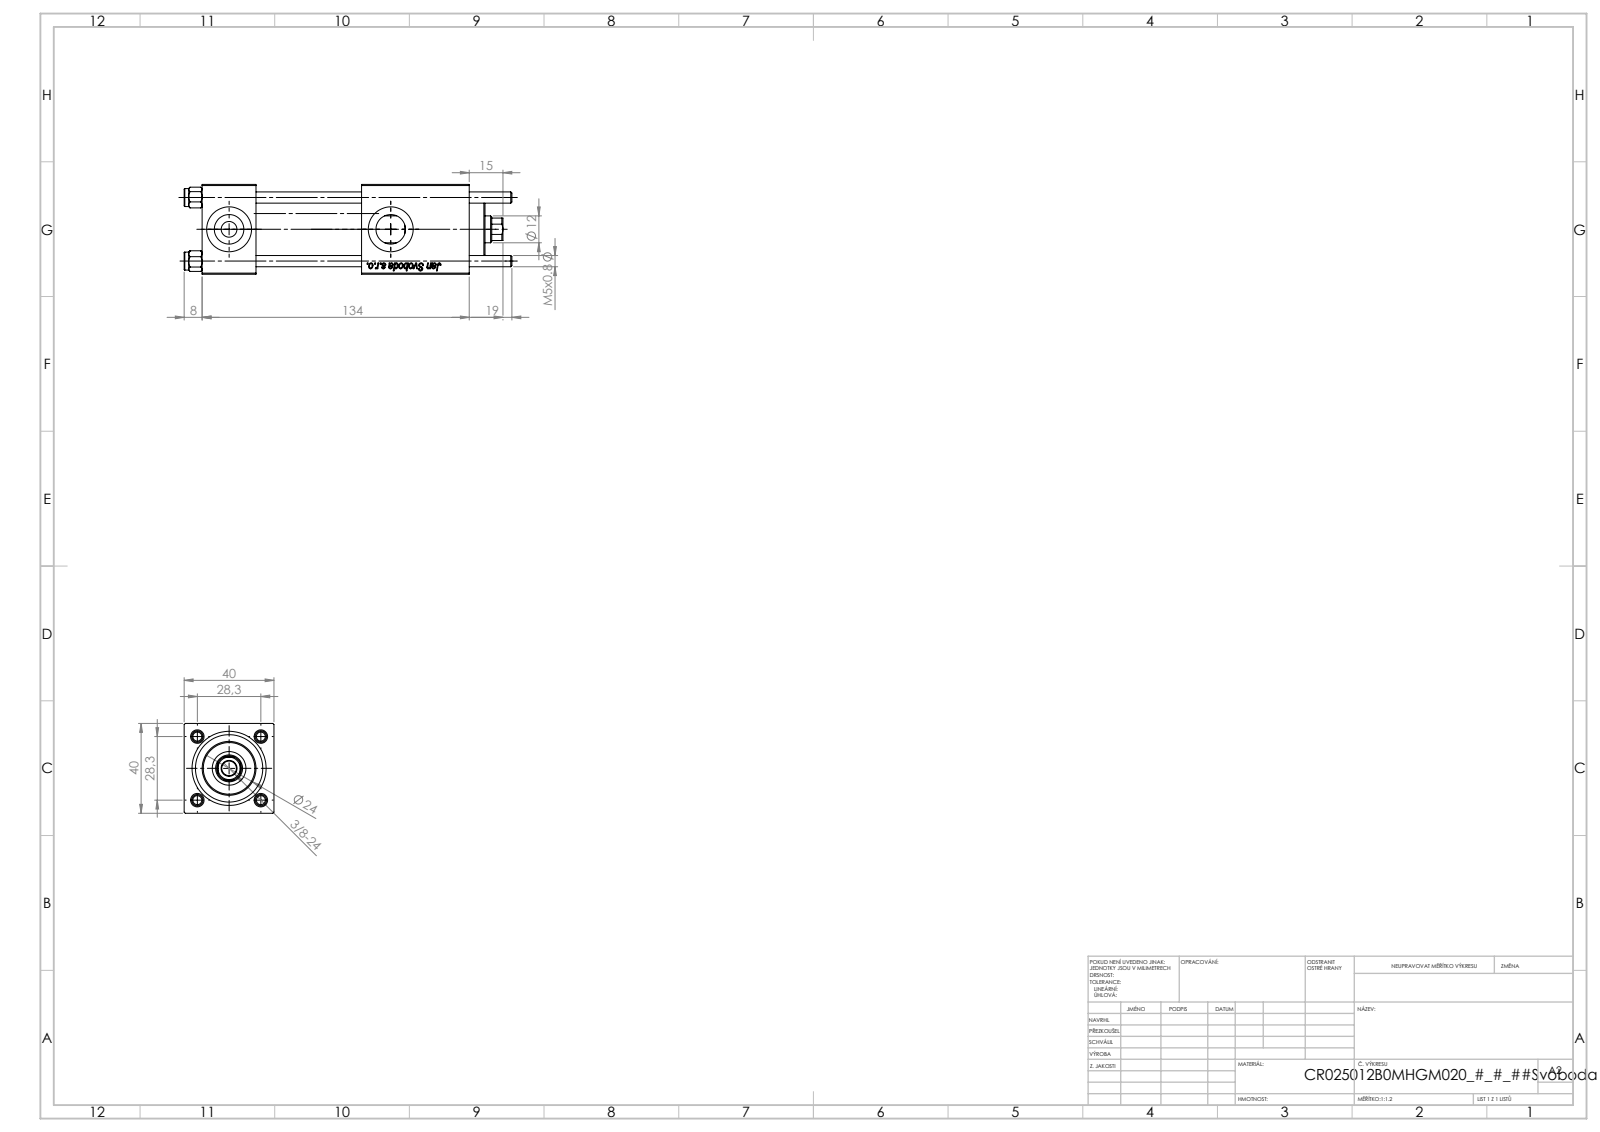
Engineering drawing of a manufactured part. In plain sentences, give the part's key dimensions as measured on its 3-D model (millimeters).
The part is named "NUT_M5_B; V215CR_B-1; V215CR_B_TYCINKA; V215CR_VCP_B (+1 more)". Its 3-D file was written by "SolidWorks 2019 (CONFIG_CONTROL_DESIGN)". It is 11 solids with 1155 faces: 429 planar, 78 cylindrical and 648 other. Overall it measures 146 by 40 by 40 millimeters. Its volume is 144 884 cubic millimeters and its surface area 58 619 square millimeters. Round holes: 4 of diameter 5, 3 of diameter 20, 2 of diameter 7, 2 of diameter 13.16, 1 of diameter 6.5, 1 of diameter 12, 1 of diameter 15, 1 of diameter 25, 1 of diameter 30. Round bosses or shafts: 4 of diameter 8, 1 of diameter 31, 1 of diameter 24. Partial cylindrical surfaces (rounded edges, fillets, slot ends): 1 of radius 5.5. The main face-to-face distances are 40, 24, 90.3, 66.3, 71, 47, 19.3, 119, 95, 48. The hole center spacings are 20.01, 28.3, 40.02, 72.
